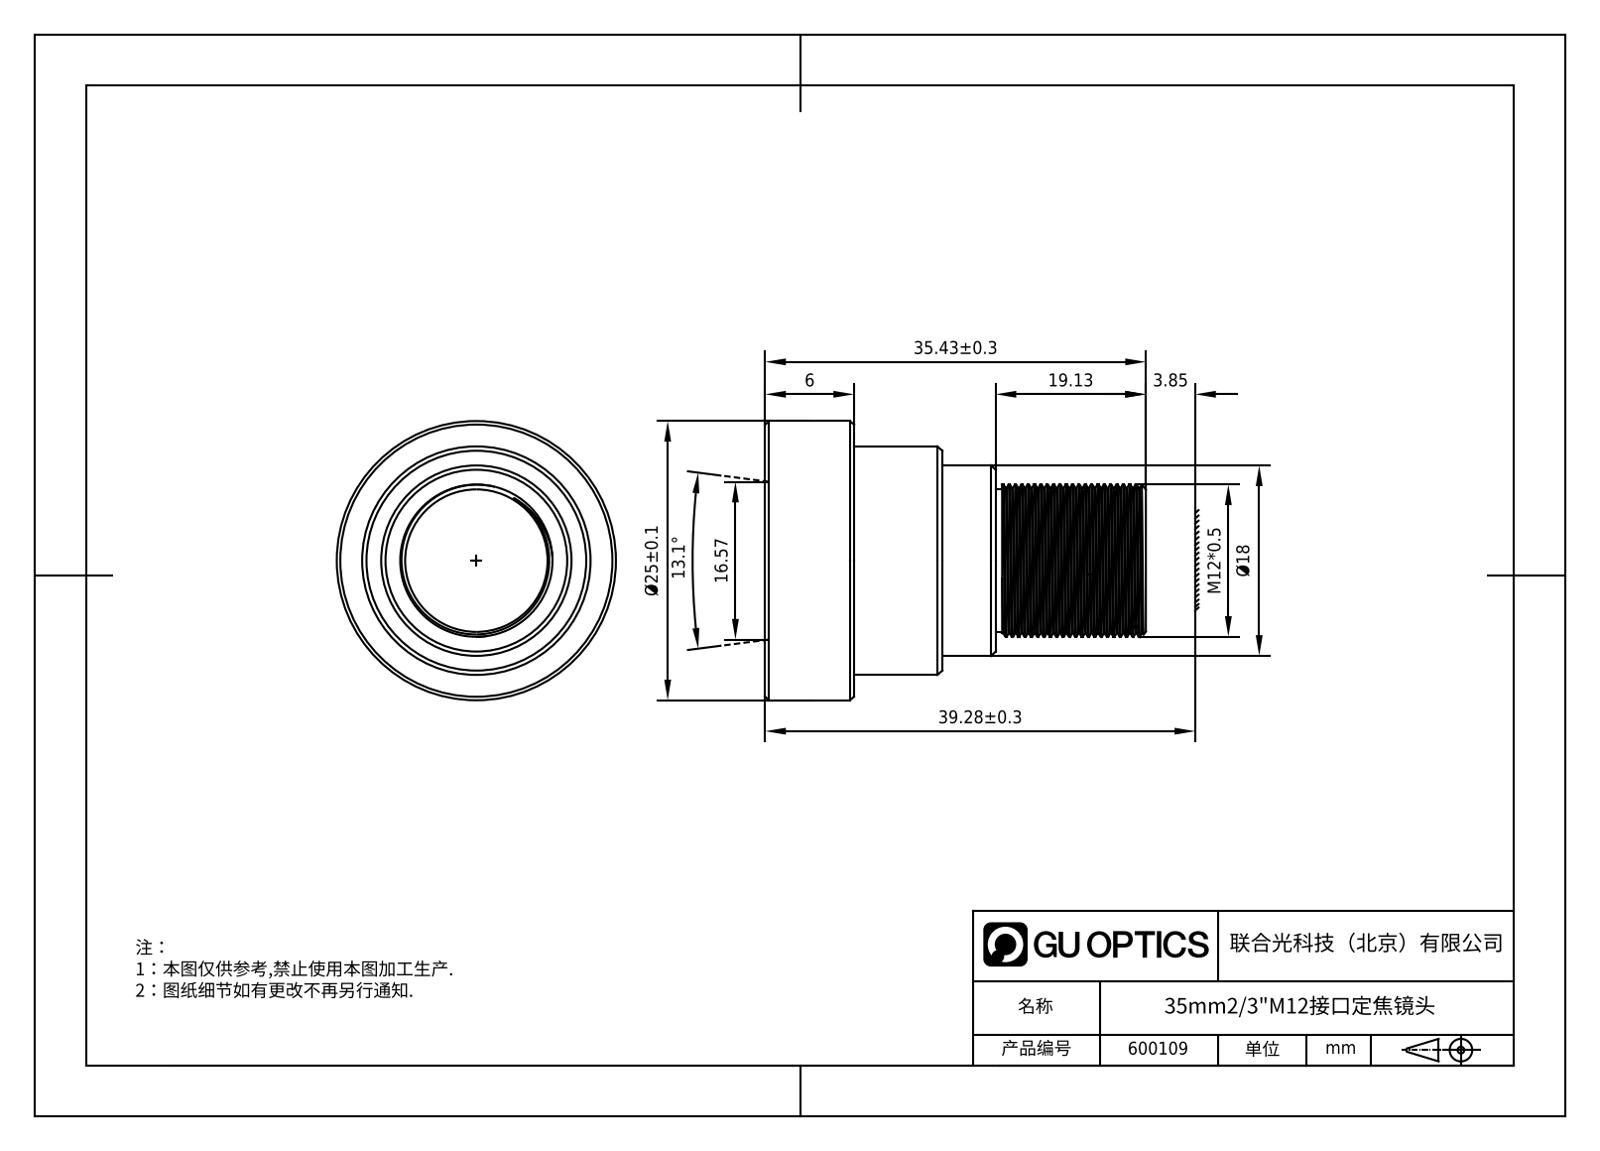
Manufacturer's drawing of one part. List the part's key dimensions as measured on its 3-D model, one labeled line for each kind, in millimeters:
Part name (STEP PRODUCT): 600109
STEP written by: SolidWorks 2020 (CONFIG_CONTROL_DESIGN)
Units: millimetres
Bodies: 1 solid, 37 faces (6 planar, 5 cylindrical, 26 other)
Overall size (bounding box): 30 × 22 × 22
Volume: 6 438 mm³ · Surface area: 2 484 mm²
Round bosses / shafts (diameter × count): ⌀22 ×1, ⌀18 ×1, ⌀15 ×1, ⌀12 ×1, ⌀11.23 ×1
Main face-to-face distances: 7, 30, 23, 18.16, 11.16, 11.84, 13.96, 6.96, 4.2, 16.04
